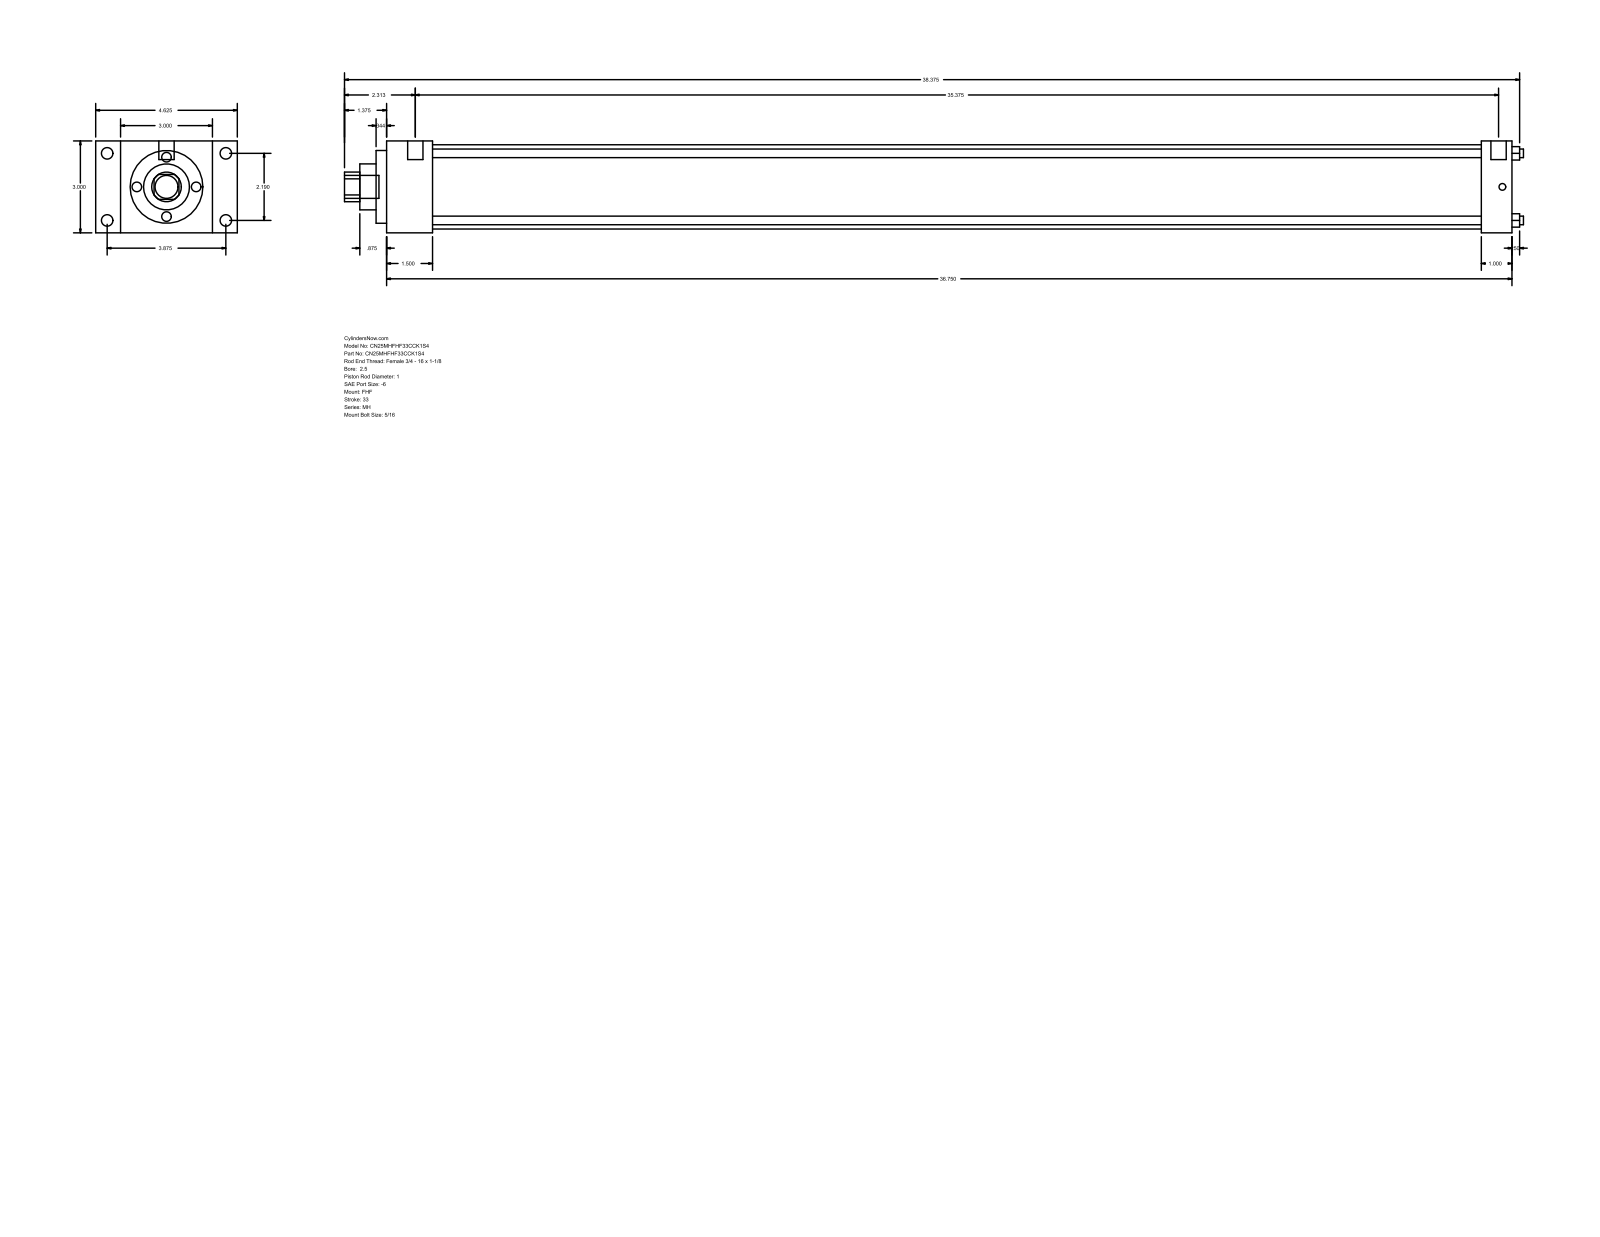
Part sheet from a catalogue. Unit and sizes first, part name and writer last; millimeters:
Units: millimetres
Overall size (bounding box): 977.9 × 117.47 × 76.2
Round holes (diameter × count): ⌀7.14 ×4, ⌀25.4 ×1, ⌀38.1 ×1, ⌀60.33 ×1, ⌀69.85 ×1
Round bosses / shafts (diameter × count): ⌀9.53 ×4, ⌀5.56 ×4, ⌀12.7 ×2, ⌀19.05 ×1
Partial cylindrical surfaces — rounded edges, fillets, slot ends (radius × count): R12.29 ×1
Main face-to-face distances: 76.2, 933.46, 38.11, 895.35, 20.64, 96.84, 117.48, 908.06, 869.95, 25.4
Hole centre spacings: 39.33, 55.62, 78.66
Bodies: 0 solids, 90 faces (61 planar, 29 cylindrical, 0 other)
Part name (STEP PRODUCT): MH_FHF__0250_1
STEP written by: GSSL Pune (CONFIG_CONTROL_DESIGN)
